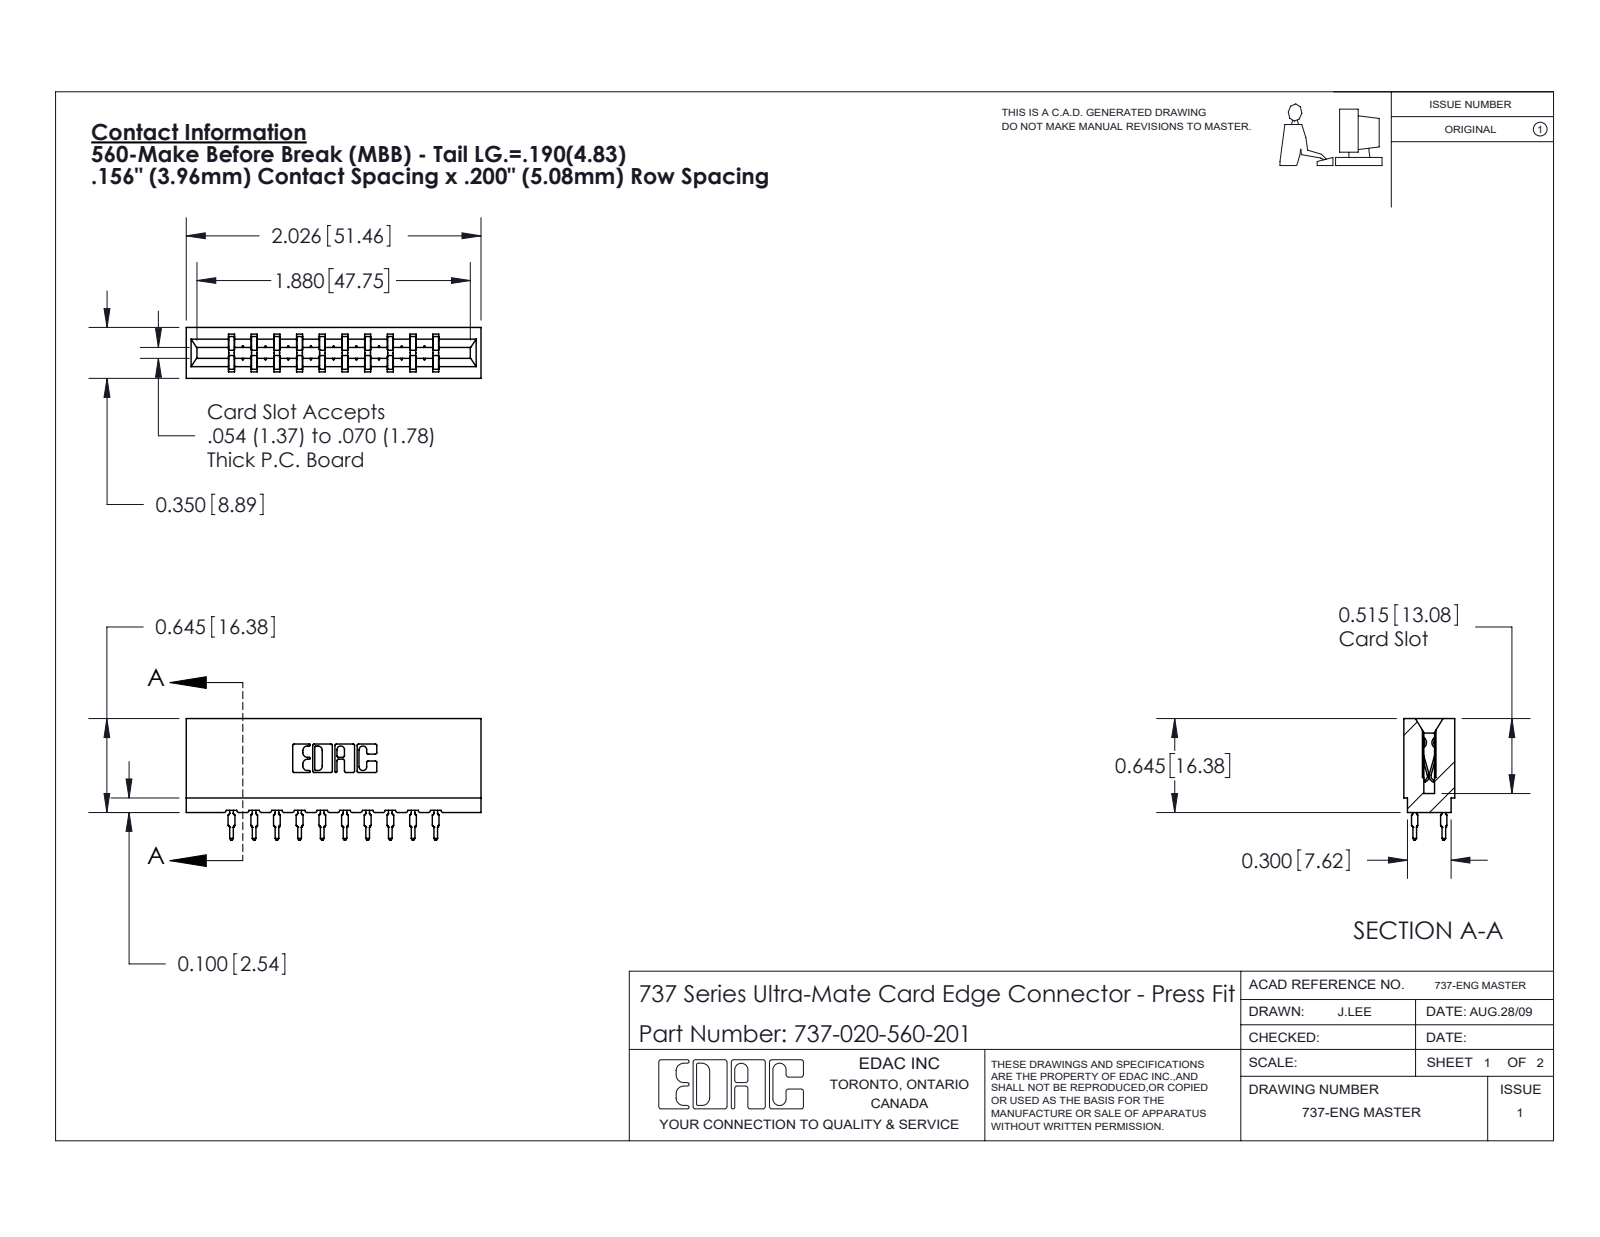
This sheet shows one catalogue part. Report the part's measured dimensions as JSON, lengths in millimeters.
{"part_name": "737-020-560-201; 737 Part_Insulator Option - 01; 745-292-001_560", "step_written_by": "SolidWorks 2020 (CONFIG_CONTROL_DESIGN)", "units": "millimeters", "bodies": {"solids": 21, "faces": 2074, "planar": 1084, "cylindrical": 470, "other": 520}, "overall_size": [51.5, 21.2, 8.9], "volume_mm3": 5360, "surface_area_mm2": 7439, "partial_cylinders_radius": [[0.5, 40], [0.3, 22], [0.4, 20], [0.1, 8], [0.3, 8], [0.2, 6], [0.8, 6], [0.7, 3]], "face_to_face_distances": [4, 3.5, 5.4, 8.9, 15.8, 7.9, 9, 19.8, 11.9, 5]}
